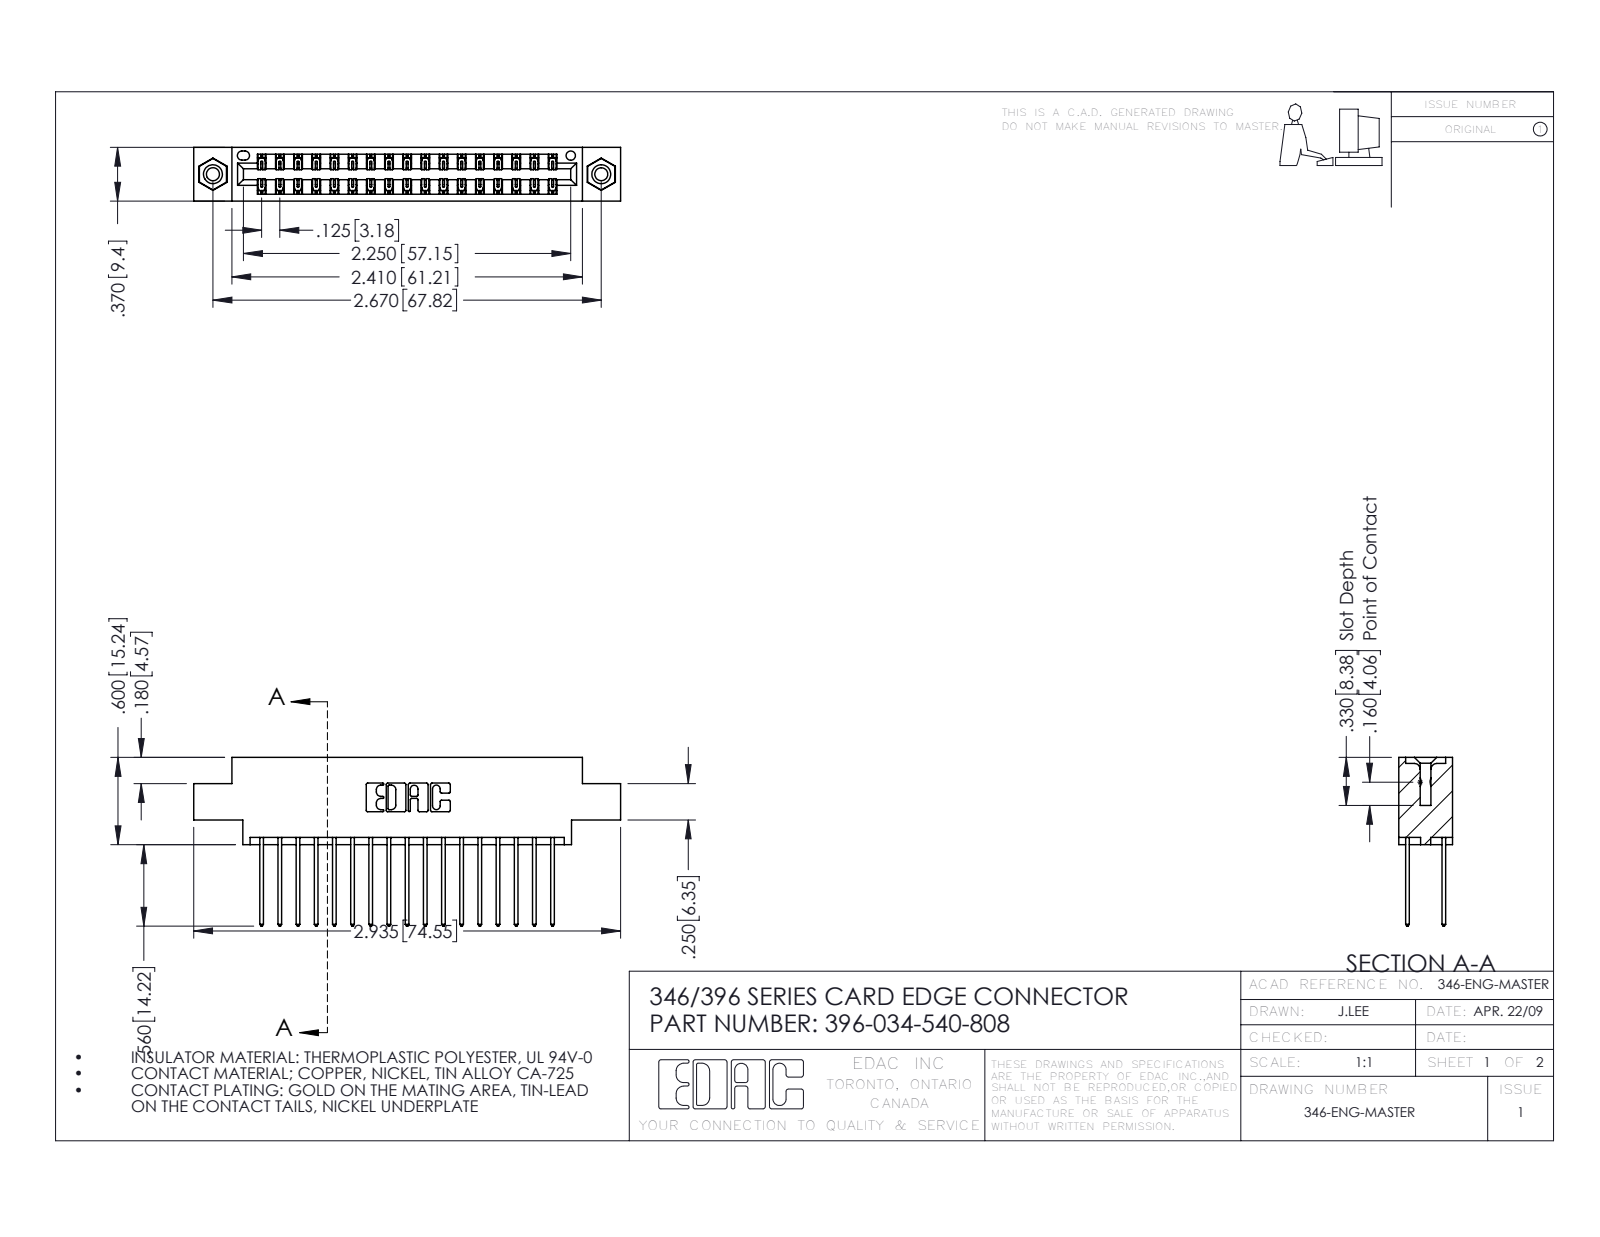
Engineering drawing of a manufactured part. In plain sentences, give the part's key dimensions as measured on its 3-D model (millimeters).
The part is named "345-250-001_345-250-003-102; 345-292-001_345-293-140; 346 Part_0.170 Offset - 0.156 Dia-TI; 396-034-540-808". Its 3-D file was written by "SolidWorks 2016 (CONFIG_CONTROL_DESIGN)". It is 37 solids with 1954 faces: 1302 planar, 636 cylindrical and 16 other. Overall it measures 74.5 by 29.5 by 9.4 millimeters. Its volume is 7 050 cubic millimeters and its surface area 10 100 square millimeters. Round holes: 2 of diameter 2.3, 2 of diameter 3.2, 2 of diameter 4, 1 of diameter 1.6. Round bosses or shafts: 2 of diameter 3.9. Partial cylindrical surfaces (rounded edges, fillets, slot ends): 51 of radius 0.2, 34 of radius 0.3, 22 of radius 0.3, 6 of radius 0.2, 6 of radius 0.8, 3 of radius 0.7, 2 of radius 0.4, 2 of radius 0.6. The main face-to-face distances are 1.2, 8.2, 6.4, 9.4, 1.8, 7.6, 0.6, 7, 5.6, 3.8. The hole center spacings are 6.2, 62.6, 67.8.
